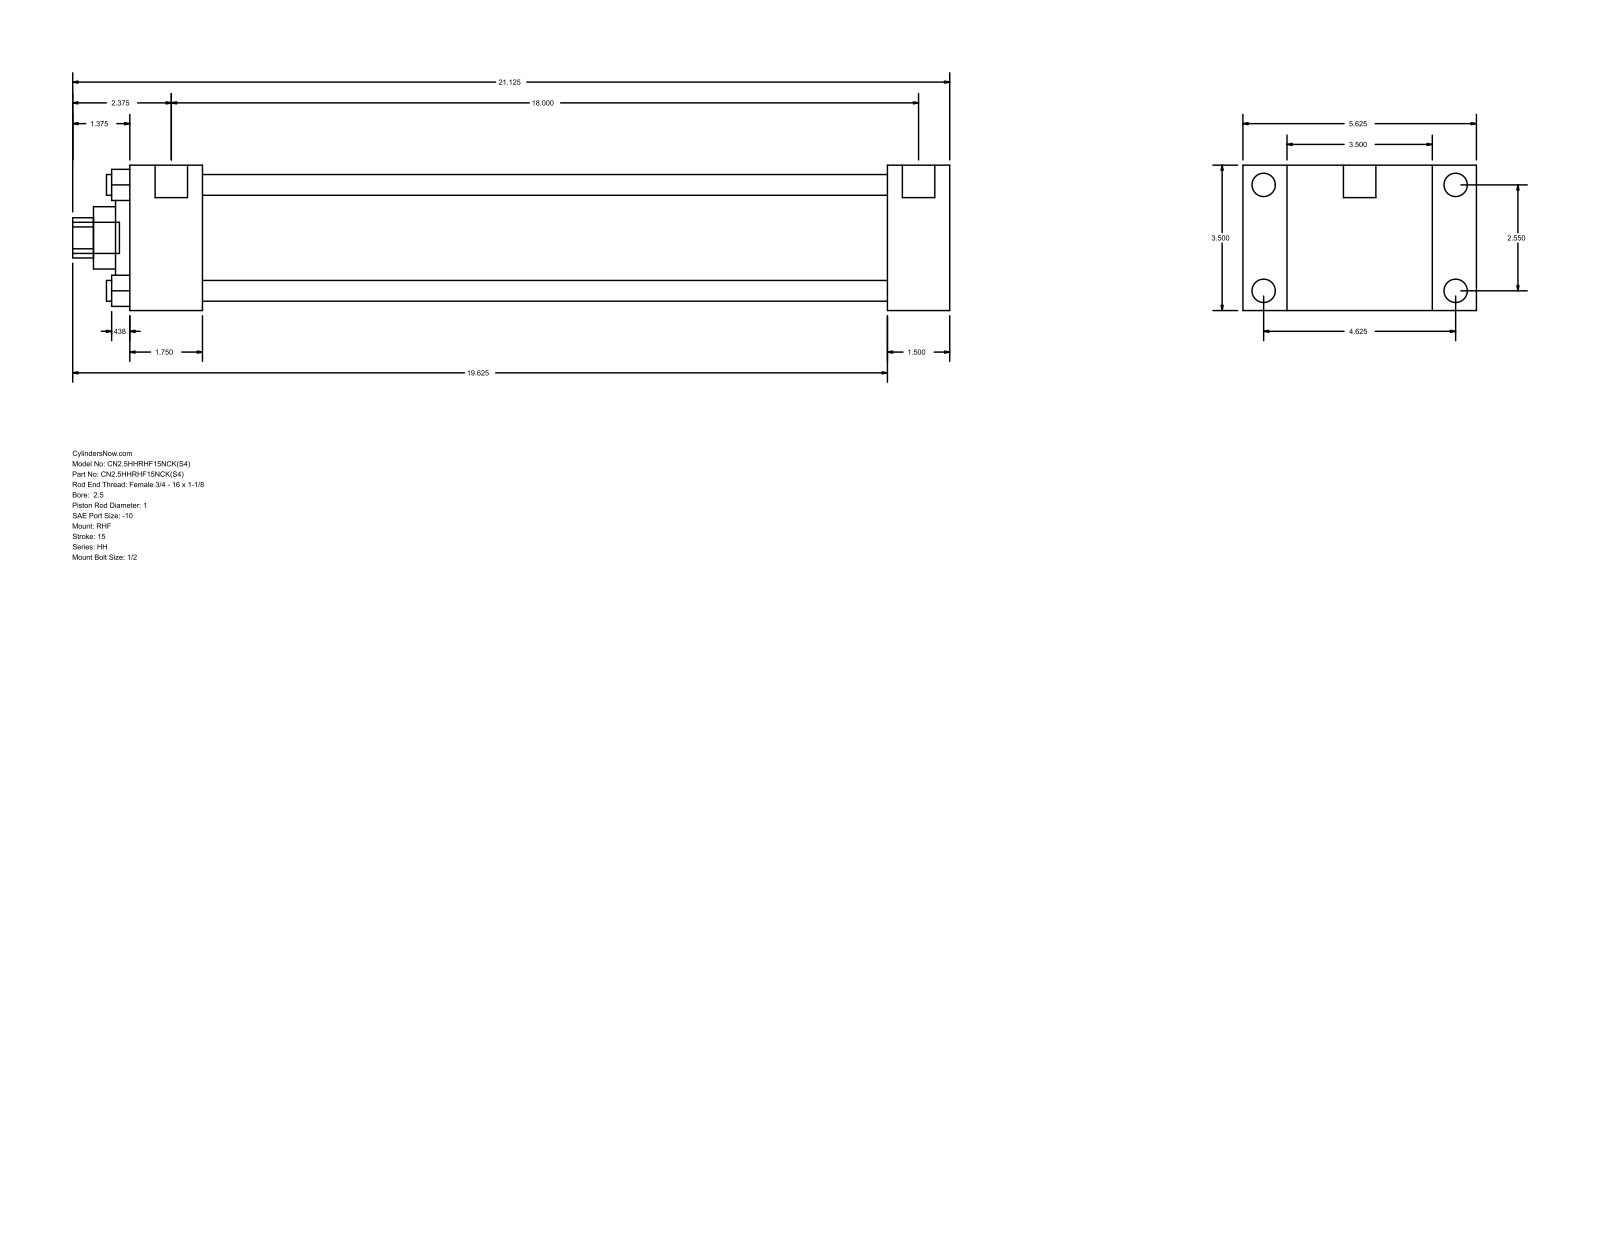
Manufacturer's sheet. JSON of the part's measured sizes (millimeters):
{"part_name": "HH_RHF__0250_1", "step_written_by": "GSSL Pune (CONFIG_CONTROL_DESIGN)", "units": "millimeters", "bodies": {"solids": 0, "faces": 90, "planar": 61, "cylindrical": 29, "other": 0}, "overall_size": [536.58, 142.88, 88.9], "round_holes": [[12.7, 4], [25.4, 1], [38.1, 1], [60.33, 1], [73.03, 1]], "round_bosses_or_shafts": [[14.3, 4], [5.56, 4], [19.84, 2], [19.05, 1]], "partial_cylinders_radius": [[12.29, 1]], "face_to_face_distances": [88.9, 38.1, 26.99, 115.89, 463.56, 501.66, 142.88, 44.46, 419.1, 457.2], "hole_center_spacings": [45.79, 64.76, 91.58]}
